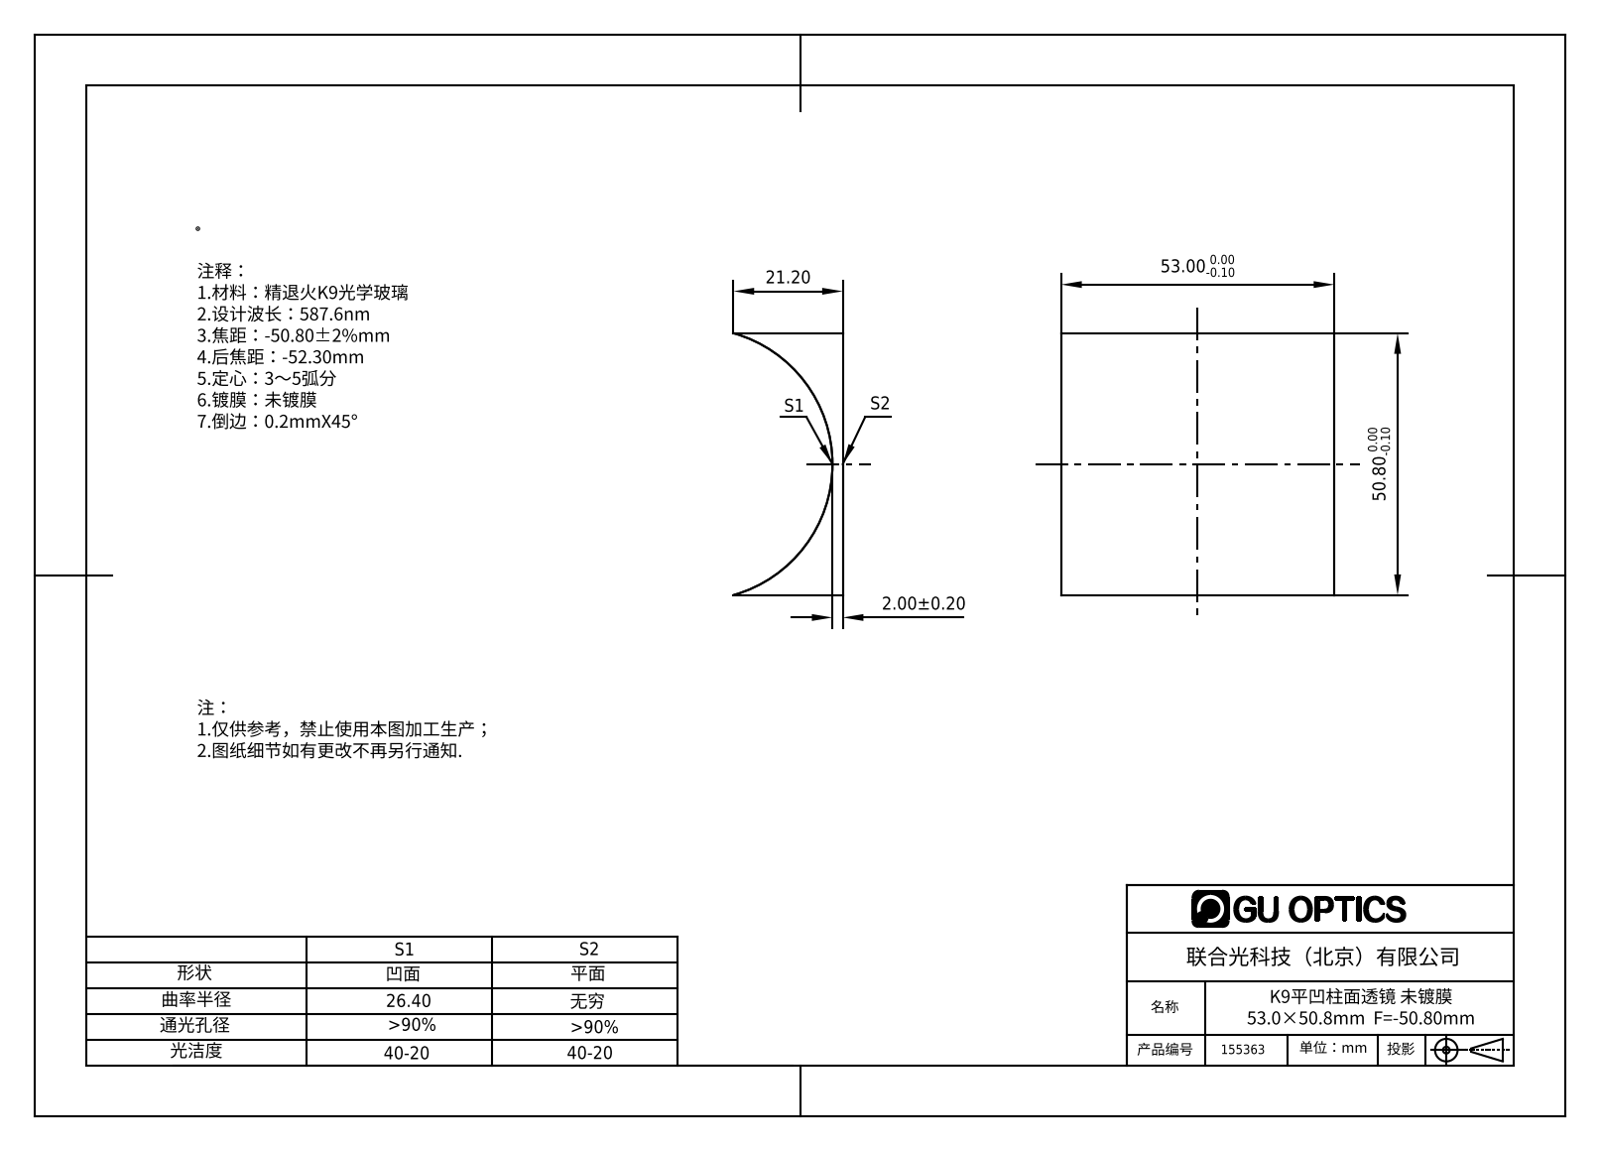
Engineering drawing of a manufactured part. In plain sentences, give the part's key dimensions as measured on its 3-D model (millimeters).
The part is named "155363". Its 3-D file was written by "SolidWorks 2016 (AUTOMOTIVE_DESIGN)". It is 1 solid with 6 faces: 5 planar, 1 cylindrical and 0 other. Overall it measures 53 by 50.8 by 21.2 millimeters. Its volume is 18 951 cubic millimeters and its surface area 9 278 square millimeters. Partial cylindrical surfaces (rounded edges, fillets, slot ends): 1 of radius 26.4. The main face-to-face distances are 50.8, 53.
